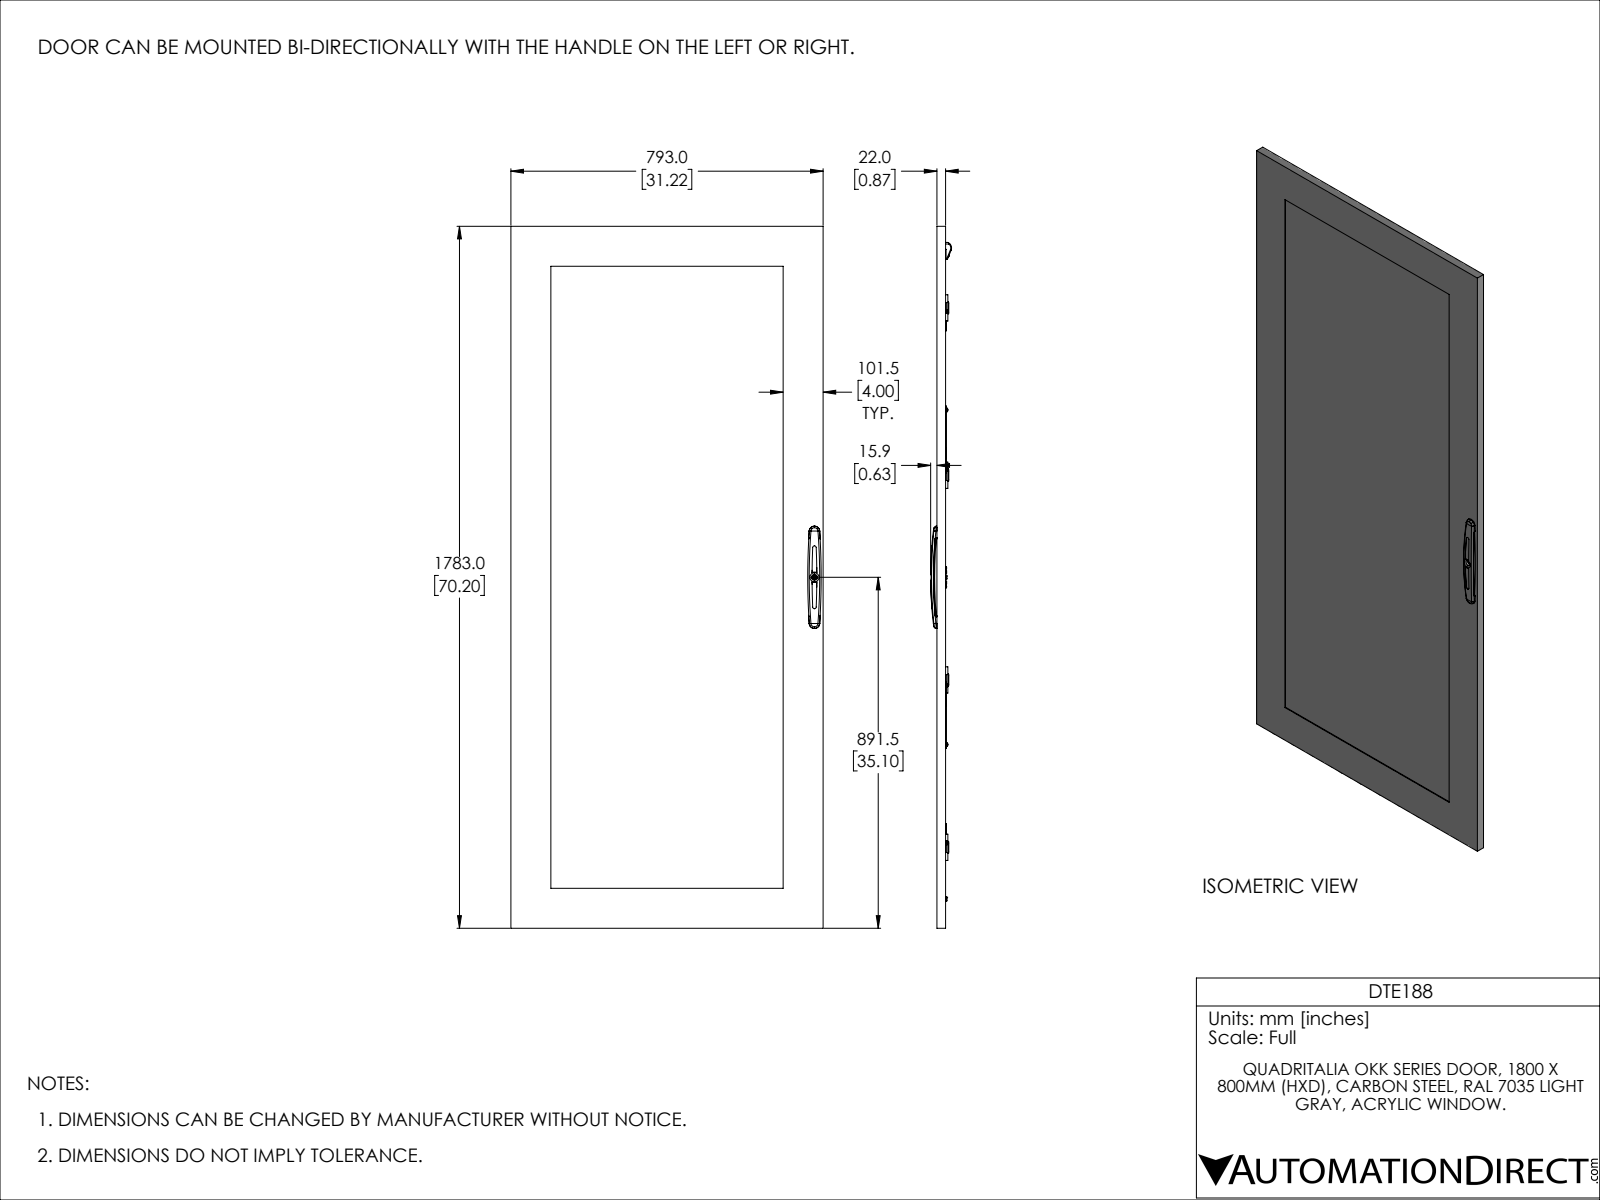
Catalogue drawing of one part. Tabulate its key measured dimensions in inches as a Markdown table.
| quantity | value |
| --- | --- |
| part name | DTE188 |
| STEP written by | SolidWorks 2021 (CONFIG_CONTROL_DESIGN) |
| units | inches |
| bodies | 102 solids, 3625 faces (1763 planar, 1233 cylindrical, 629 other) |
| overall size | 70.197 × 31.22 × 2.091 |
| volume | 397.8 in³ |
| surface area | 6 823 in² |
| round holes (diameter × count) | 0.167 × 136, 0.315 × 29, 0.354 × 18, 0.194 × 10, 0.01 × 8, 0.197 × 8, 0.194 × 4, 0.244 × 4, 0.276 × 4, 0.205 × 3, 0.134 × 2, 0.169 × 2 |
| round bosses / shafts (diameter × count) | 0.276 × 21, 0.236 × 17, 0.283 × 14, 0.394 × 10, 0.197 × 9, 0.193 × 8, 0.472 × 2, 0.315 × 2 |
| partial cylindrical surfaces (radius × count) | 0.012 × 74, 0.039 × 70, 0.059 × 36, 0.02 × 33, 0.098 × 28, 0.177 × 16, 0.079 × 15, 0.227 × 14 |
| main face-to-face distances | 0.157, 0.079, 0.236, 0.059, 0.728, 0.787, 0.669, 0.866, 25.984, 0.63 |
| hole center spacings | 0.984, 1.969, 2.953, 8.858, 3.937, 4.921, 5.906, 6.89 |
